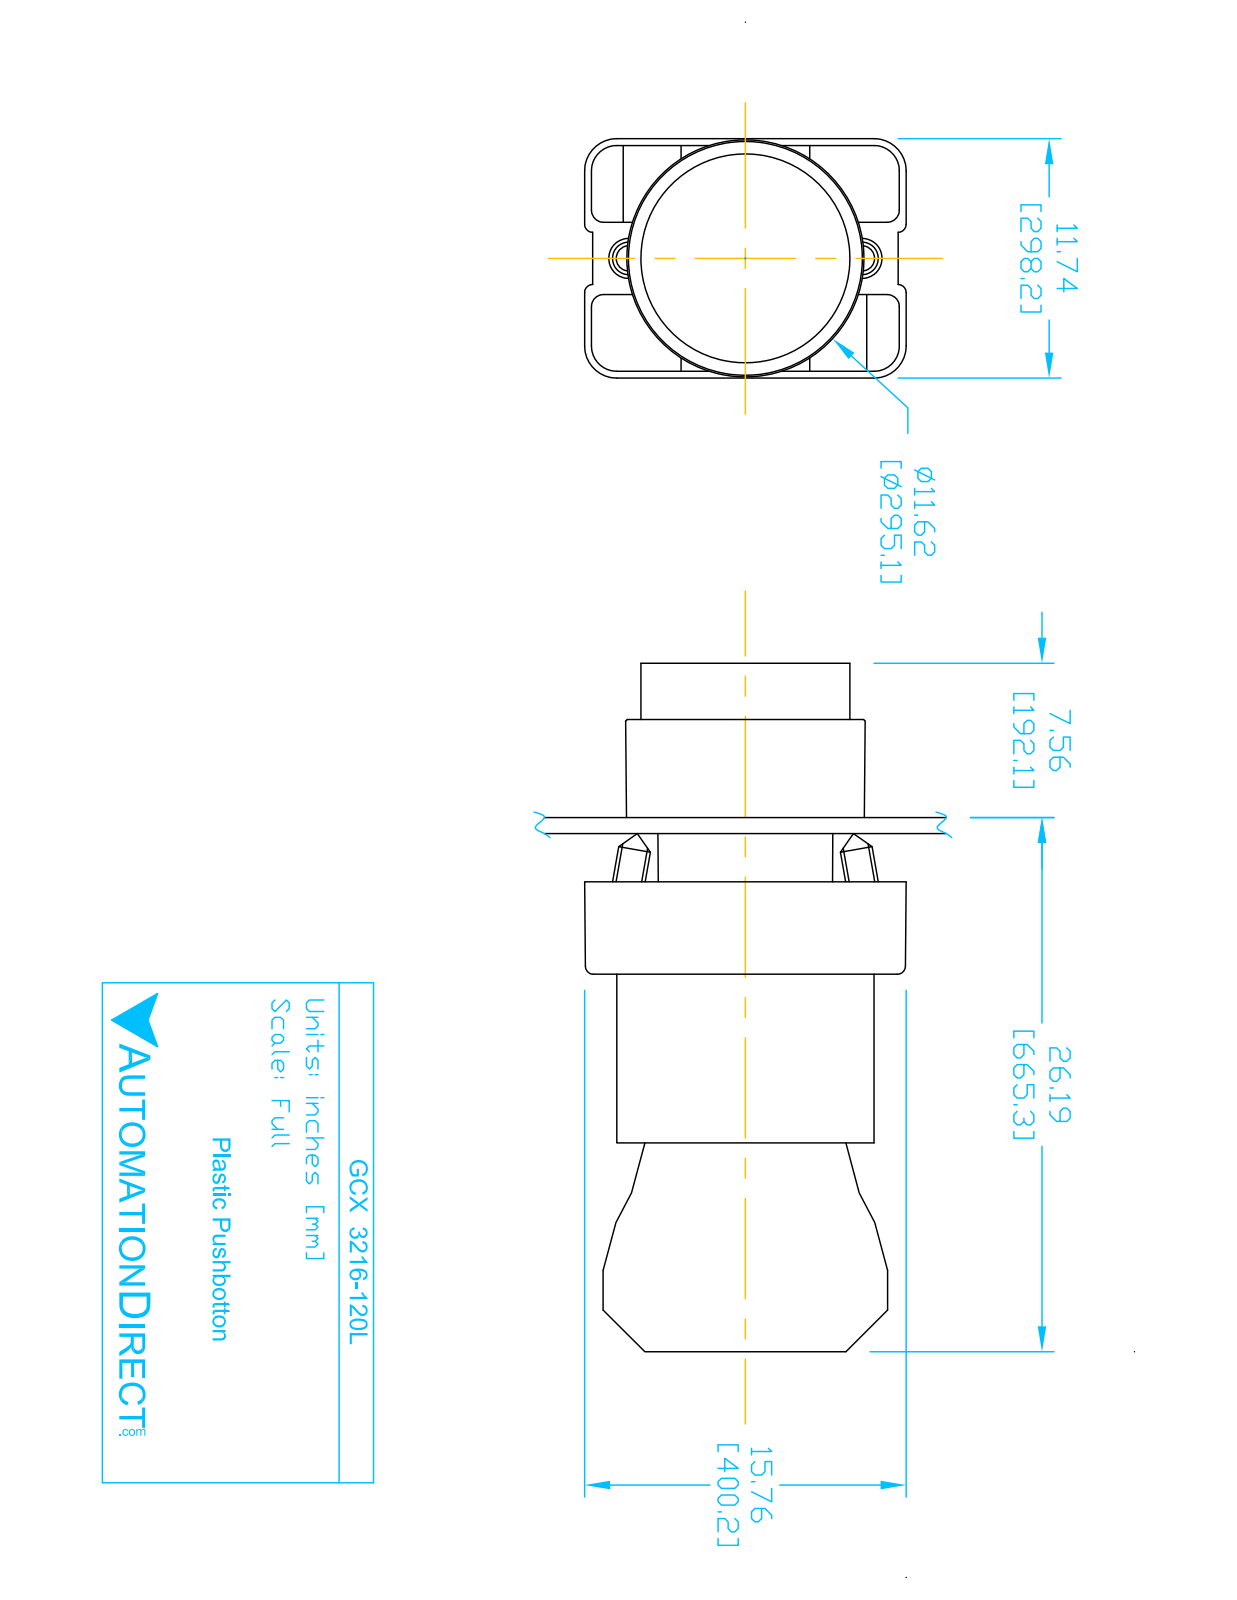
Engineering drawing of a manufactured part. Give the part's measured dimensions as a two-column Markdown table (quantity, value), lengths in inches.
| quantity | value |
| --- | --- |
| part name | ECX1050; GCX3216L OPERATOR; ecx1040; ECX3029-2 (+1 more) |
| STEP written by | SolidWorks 2016 (AUTOMOTIVE_DESIGN) |
| units | inches |
| bodies | 7 solids, 425 faces (250 planar, 144 cylindrical, 31 other) |
| overall size | 3.319 × 1.581 × 1.177 |
| volume | 2.721 in³ |
| surface area | 36.32 in² |
| round holes (diameter × count) | 0.079 × 2, 0.124 × 2, 0.13 × 2, 0.087 × 1, 0.197 × 1, 0.469 × 1, 0.878 × 1, 0.888 × 1, 1.024 × 1 |
| round bosses / shafts (diameter × count) | 0.157 × 4, 1.175 × 1, 1.004 × 1, 0.945 × 1, 0.856 × 1, 0.78 × 1, 0.504 × 1 |
| partial cylindrical surfaces (radius × count) | 0.059 × 24, 0.041 × 12, 0.124 × 12, 0.157 × 12, 0.039 × 8, 0.128 × 2, 0.02 × 1, 0.063 × 1 |
| main face-to-face distances | 0.827, 0.579, 1.171, 2.02, 1.193, 0.031, 0.033, 0.573, 1.165, 0.593 |
| hole center spacings | 0.236, 0.544, 0.472, 0.49 |
